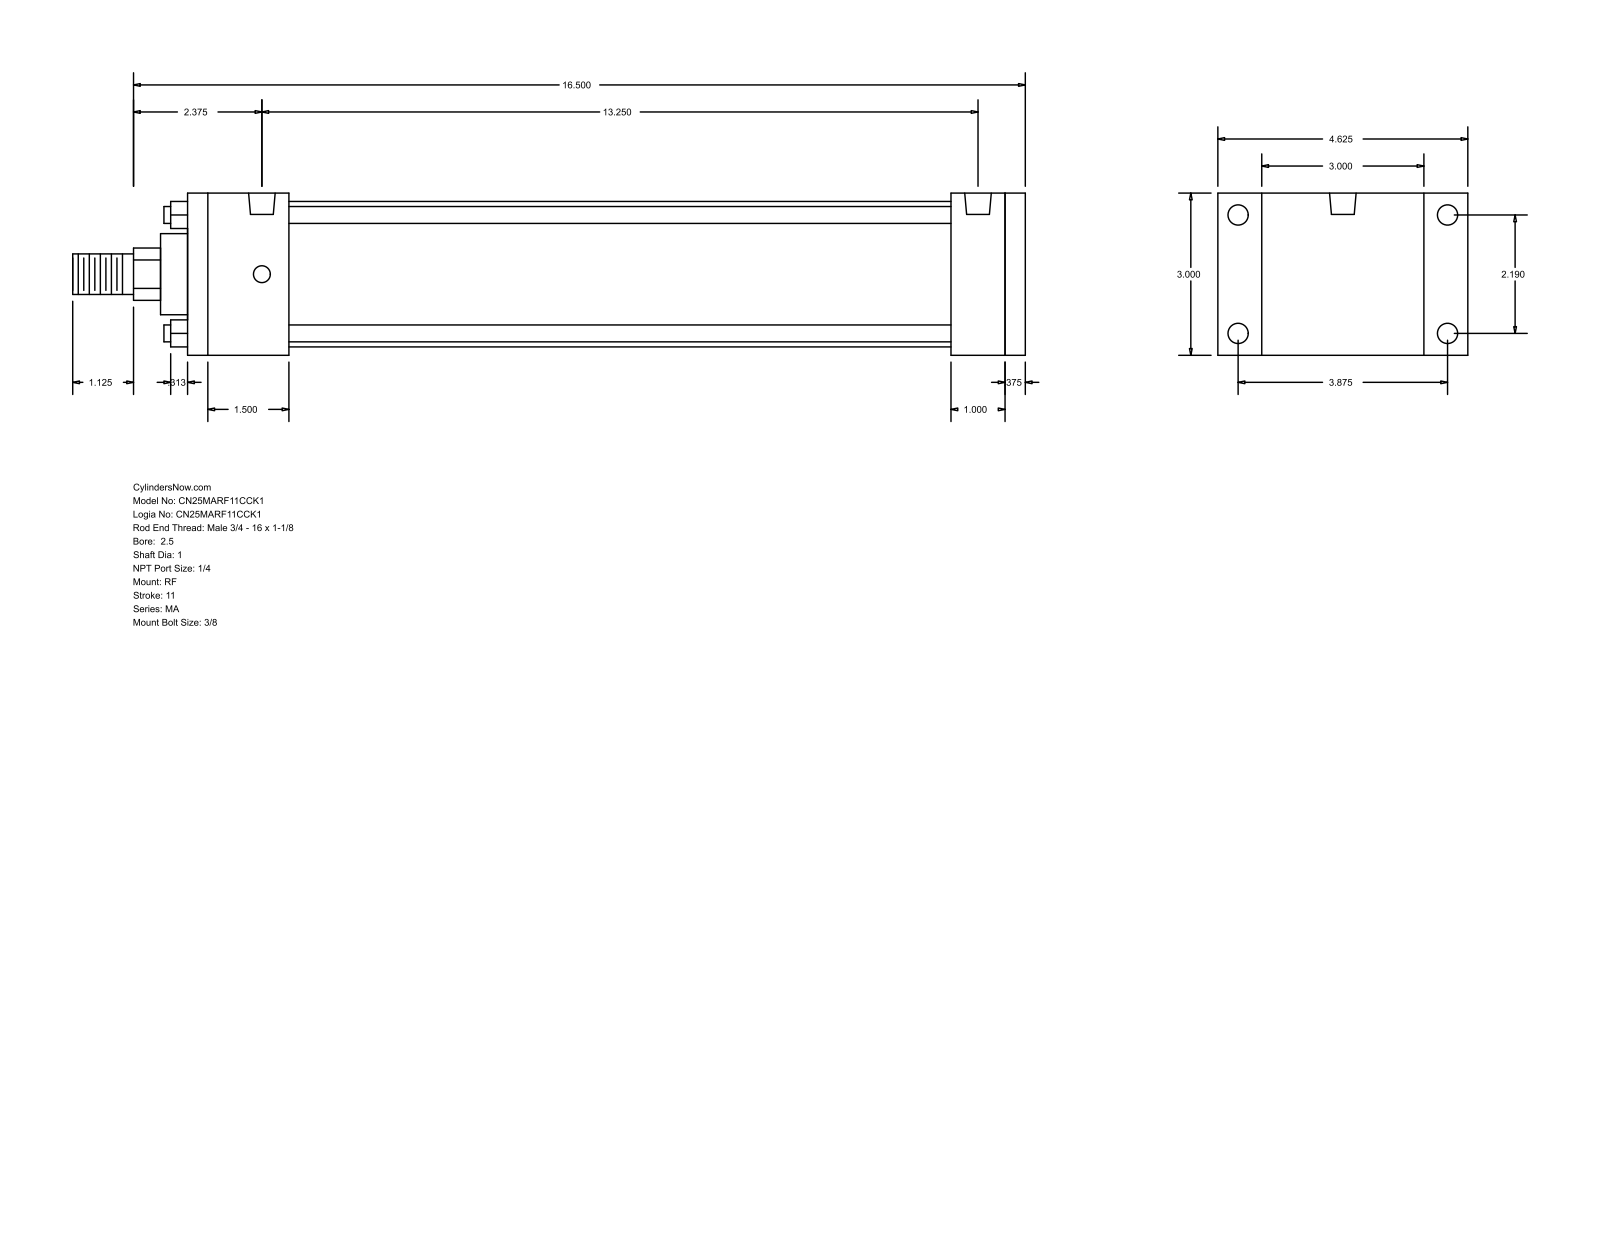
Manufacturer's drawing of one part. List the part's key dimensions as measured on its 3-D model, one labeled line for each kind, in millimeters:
Part name (STEP PRODUCT): MA_RF__0250_1
STEP written by: GSSL Pune (CONFIG_CONTROL_DESIGN)
Units: millimetres
Bodies: 0 solids, 92 faces (64 planar, 28 cylindrical, 0 other)
Overall size (bounding box): 447.68 × 117.47 × 76.2
Round holes (diameter × count): ⌀7.94 ×4, ⌀9.53 ×4, ⌀12.49 ×2
Round bosses / shafts (diameter × count): ⌀7.94 ×4, ⌀68.33 ×1, ⌀38.1 ×1, ⌀25.4 ×1, ⌀19.05 ×1
Partial cylindrical surfaces — rounded edges, fillets, slot ends (radius × count): R12.29 ×1
Main face-to-face distances: 76.2, 393.7, 9.53, 384.17, 47.63, 358.78, 311.15, 336.54, 346.07, 25.39
Hole centre spacings: 55.62, 98.42, 113.05, 336.55
